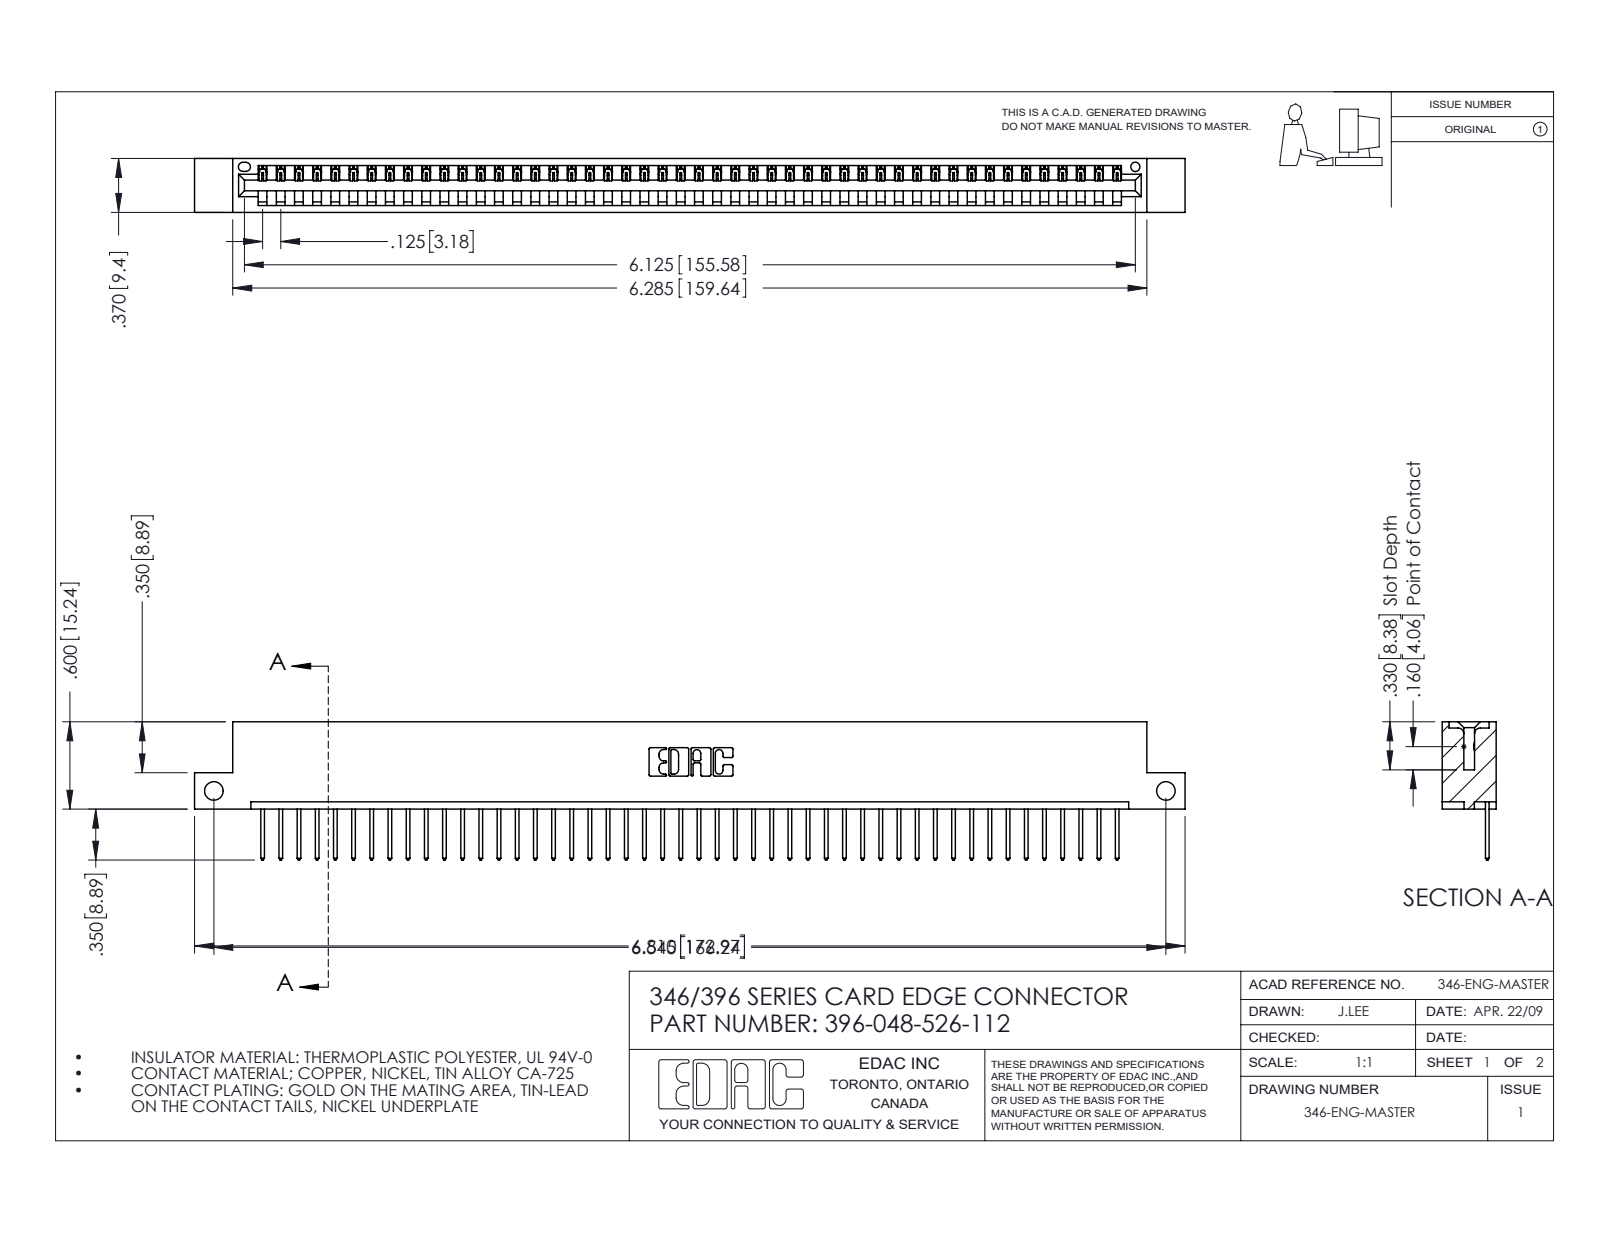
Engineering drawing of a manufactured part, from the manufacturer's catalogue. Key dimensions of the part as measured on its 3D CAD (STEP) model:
Part name (STEP PRODUCT): 346 Part_Flush Mounting Lugs - Side Mount; 345-292-001_345-293-126; 396-048-526-112
STEP written by: SolidWorks 2016 (CONFIG_CONTROL_DESIGN)
Units: inches
Bodies: 49 solids, 2906 faces (1996 planar, 910 cylindrical, 0 other)
Overall size (bounding box): 6.81 × 0.95 × 0.37
Volume: 1.005 in³ · Surface area: 31.72 in²
Round holes (diameter × count): ⌀0.128 ×2, ⌀0.064 ×1
Partial cylindrical surfaces — rounded edges, fillets, slot ends (radius × count): R0.006 ×96, R0.01 ×96, R0.01 ×22, R0.007 ×6, R0.031 ×6, R0.026 ×3, R0.031 ×2, R0.04 ×2
Main face-to-face distances: 0.048, 0.322, 0.37, 0.25, 0.072, 0.298, 0.025, 0.148, 0.222, 0.1
Hole centre spacings: 6.545
